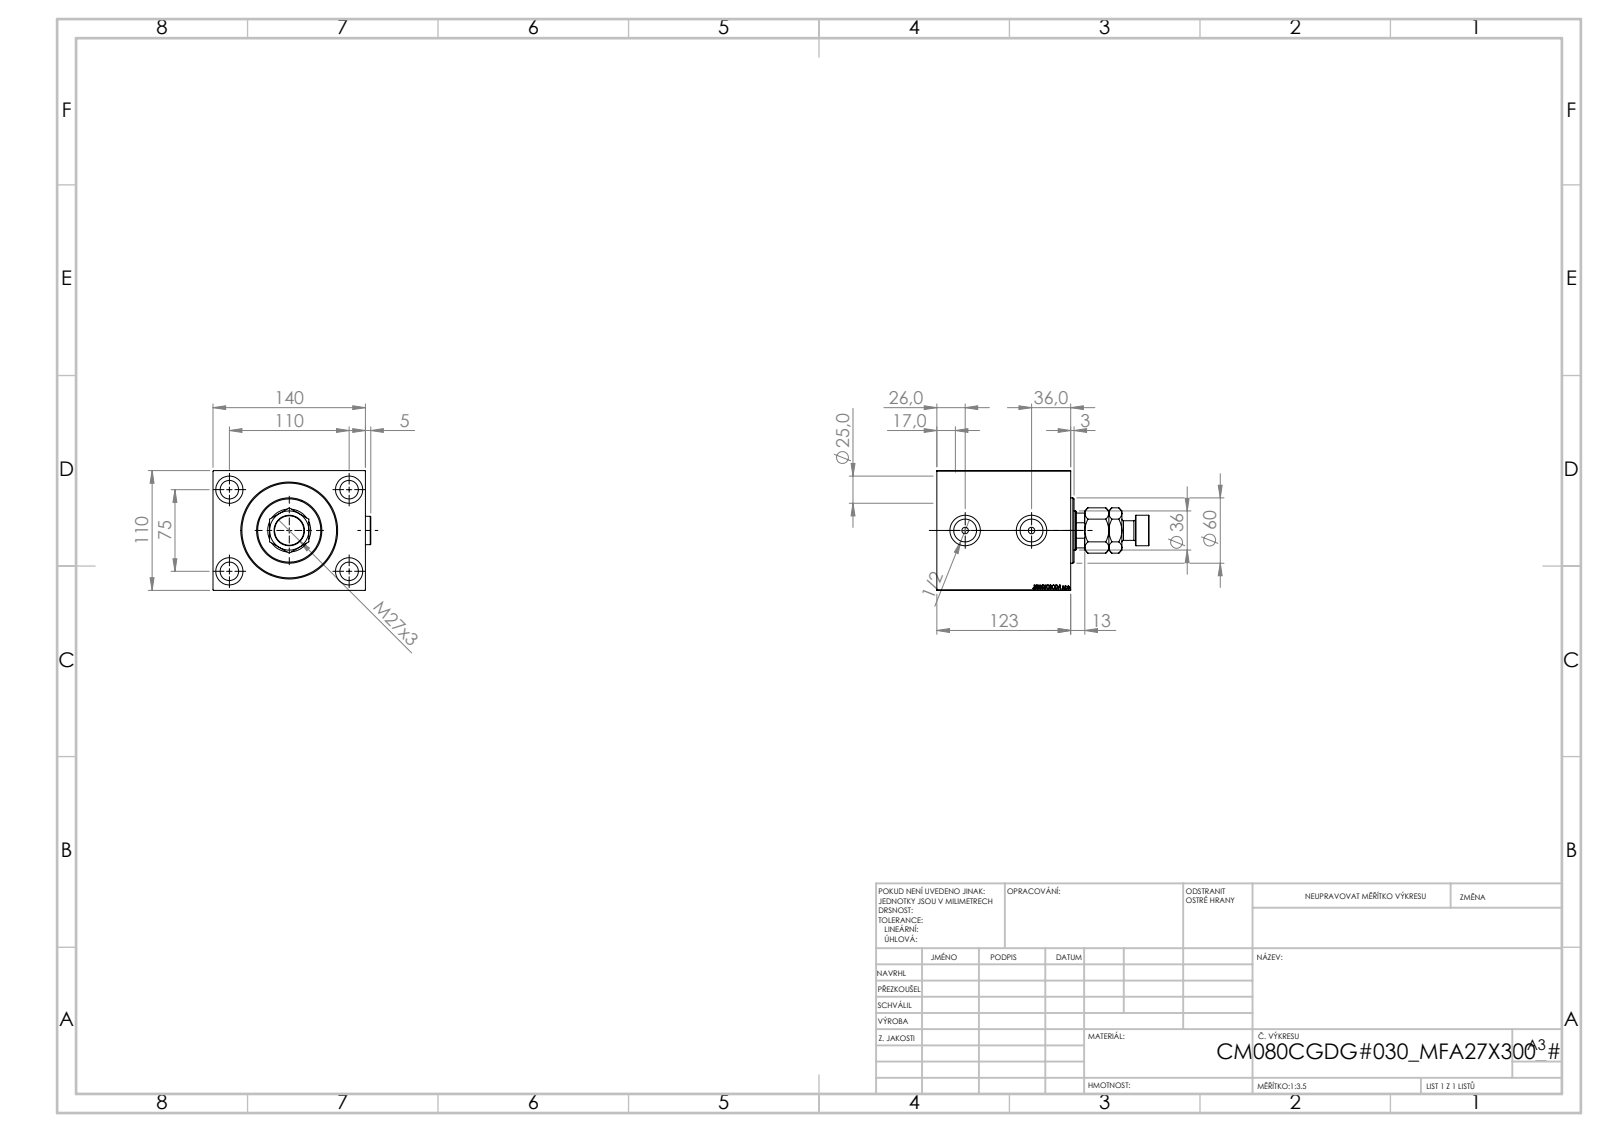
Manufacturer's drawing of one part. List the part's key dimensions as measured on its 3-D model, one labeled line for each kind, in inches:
Part name (STEP PRODUCT): Zatka_OIL_PORT; V450CM_VC_B; V450CM_C_Body; MFA (+1 more)
STEP written by: SolidWorks 2019 (CONFIG_CONTROL_DESIGN)
Units: inches
Bodies: 6 solids, 969 faces (459 planar, 80 cylindrical, 430 other)
Overall size (bounding box): 7.677 × 5.705 × 4.331
Volume: 106 in³ · Surface area: 298 in²
Round holes (diameter × count): ⌀0.669 ×4, ⌀0.984 ×4, ⌀0.236 ×2, ⌀0.825 ×2, ⌀1.102 ×2, ⌀1.004 ×1, ⌀1.417 ×1, ⌀1.555 ×1, ⌀3.15 ×1, ⌀3.228 ×1, ⌀3.425 ×1
Round bosses / shafts (diameter × count): ⌀1.024 ×2, ⌀2.362 ×1, ⌀1.102 ×1, ⌀0.709 ×1
Partial cylindrical surfaces — rounded edges, fillets, slot ends (radius × count): R0.689 ×1
Main face-to-face distances: 4.331, 5.512, 4.843, 2.835, 2.008, 0.394, 0.85, 1.157, 3.992, 1.244
Hole centre spacings: 2.621, 2.953, 4.331, 5.242, 2.402
